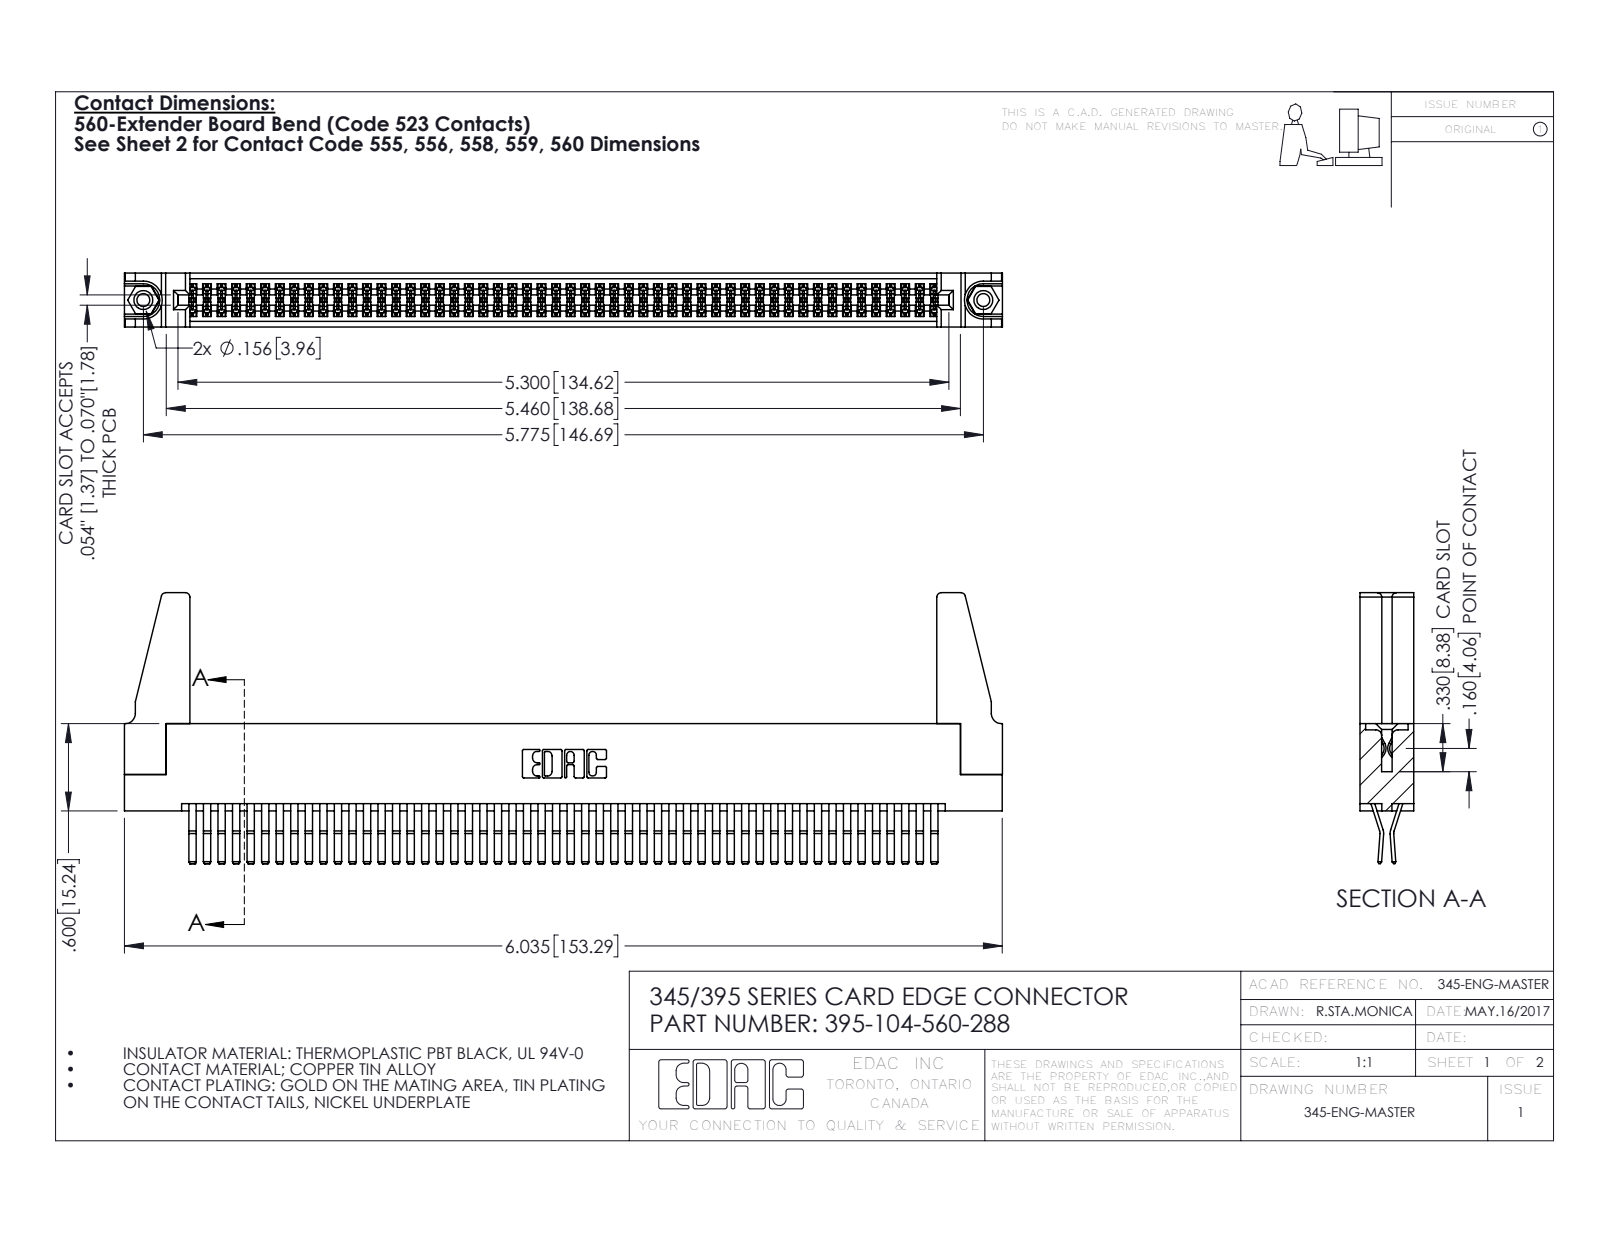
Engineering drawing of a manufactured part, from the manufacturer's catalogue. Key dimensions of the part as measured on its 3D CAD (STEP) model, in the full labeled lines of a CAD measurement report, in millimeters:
Part name (STEP PRODUCT): 345-250-001_345-250-001-102; 345 Part_Flush Mounting Lugs - 0.156 Dia-TH; 345-292-001_560 Tail; 345-220-078_345-220-088 (+1 more)
STEP written by: SolidWorks 2016 (CONFIG_CONTROL_DESIGN)
Units: millimetres
Bodies: 109 solids, 5658 faces (3584 planar, 2058 cylindrical, 16 other)
Overall size (bounding box): 153.3 × 47.3 × 9.4
Volume: 18 930 mm³ · Surface area: 28 230 mm²
Round holes (diameter × count): ⌀2.3 ×2, ⌀3.2 ×2, ⌀4 ×2, ⌀1.6 ×1
Round bosses / shafts (diameter × count): ⌀3.9 ×2
Partial cylindrical surfaces — rounded edges, fillets, slot ends (radius × count): R0.2 ×157, R0.3 ×22, R0.8 ×8, R0.2 ×6, R0.8 ×6, R0.7 ×3, R0.3 ×2, R0.4 ×2
Main face-to-face distances: 1.8, 7.6, 0.6, 9.4, 5.1, 2.5, 6.9, 5.7, 4.4, 3.8
Hole centre spacings: 6.9, 140.7, 146.7
